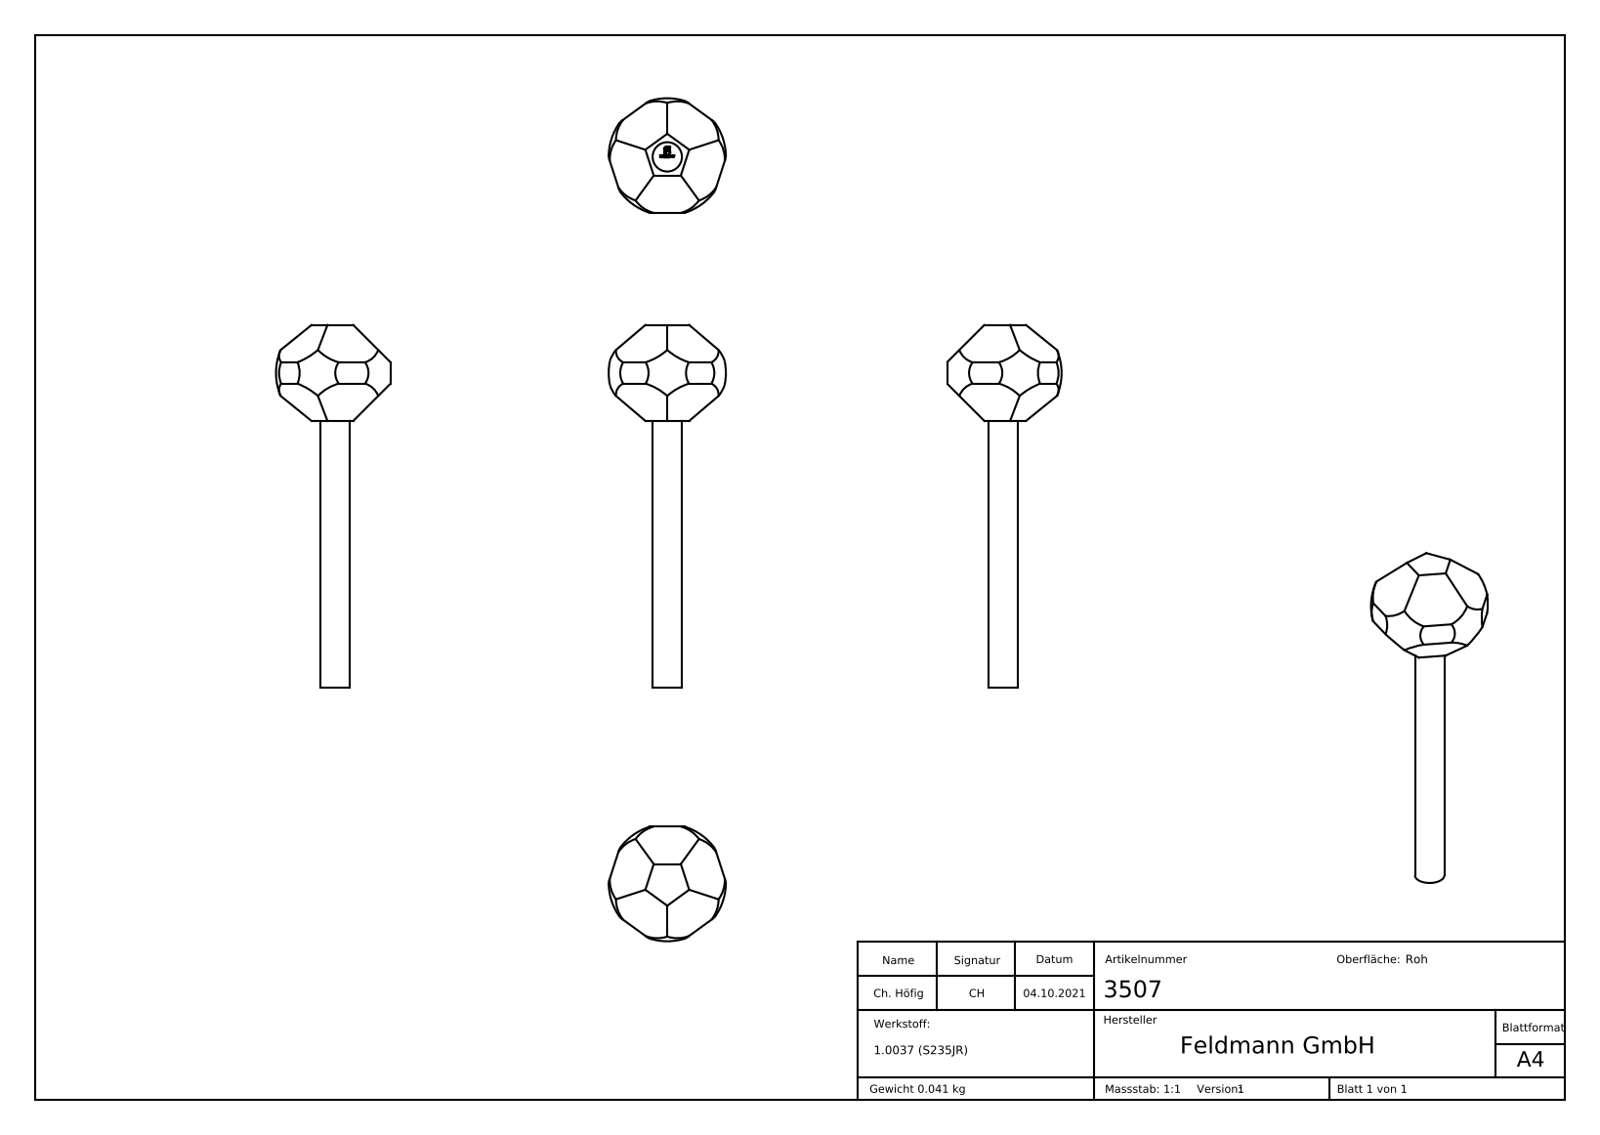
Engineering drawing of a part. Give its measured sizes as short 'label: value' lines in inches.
name: 3507
written by: SolidWorks 2018 (CONFIG_CONTROL_DESIGN)
unit: in
bodies: 1 solid, 231 faces (126 planar, 1 cylindrical, 104 other)
size: 2.677 × 0.866 × 0.846
volume: 0.324 in³; area: 3.381 in²
bosses: 1× ⌀0.217
face distances: 2.677, 1.969, 0.709, 1.965, 2.673, 0.029, 0.025, 0.032, 0.022, 0.019
